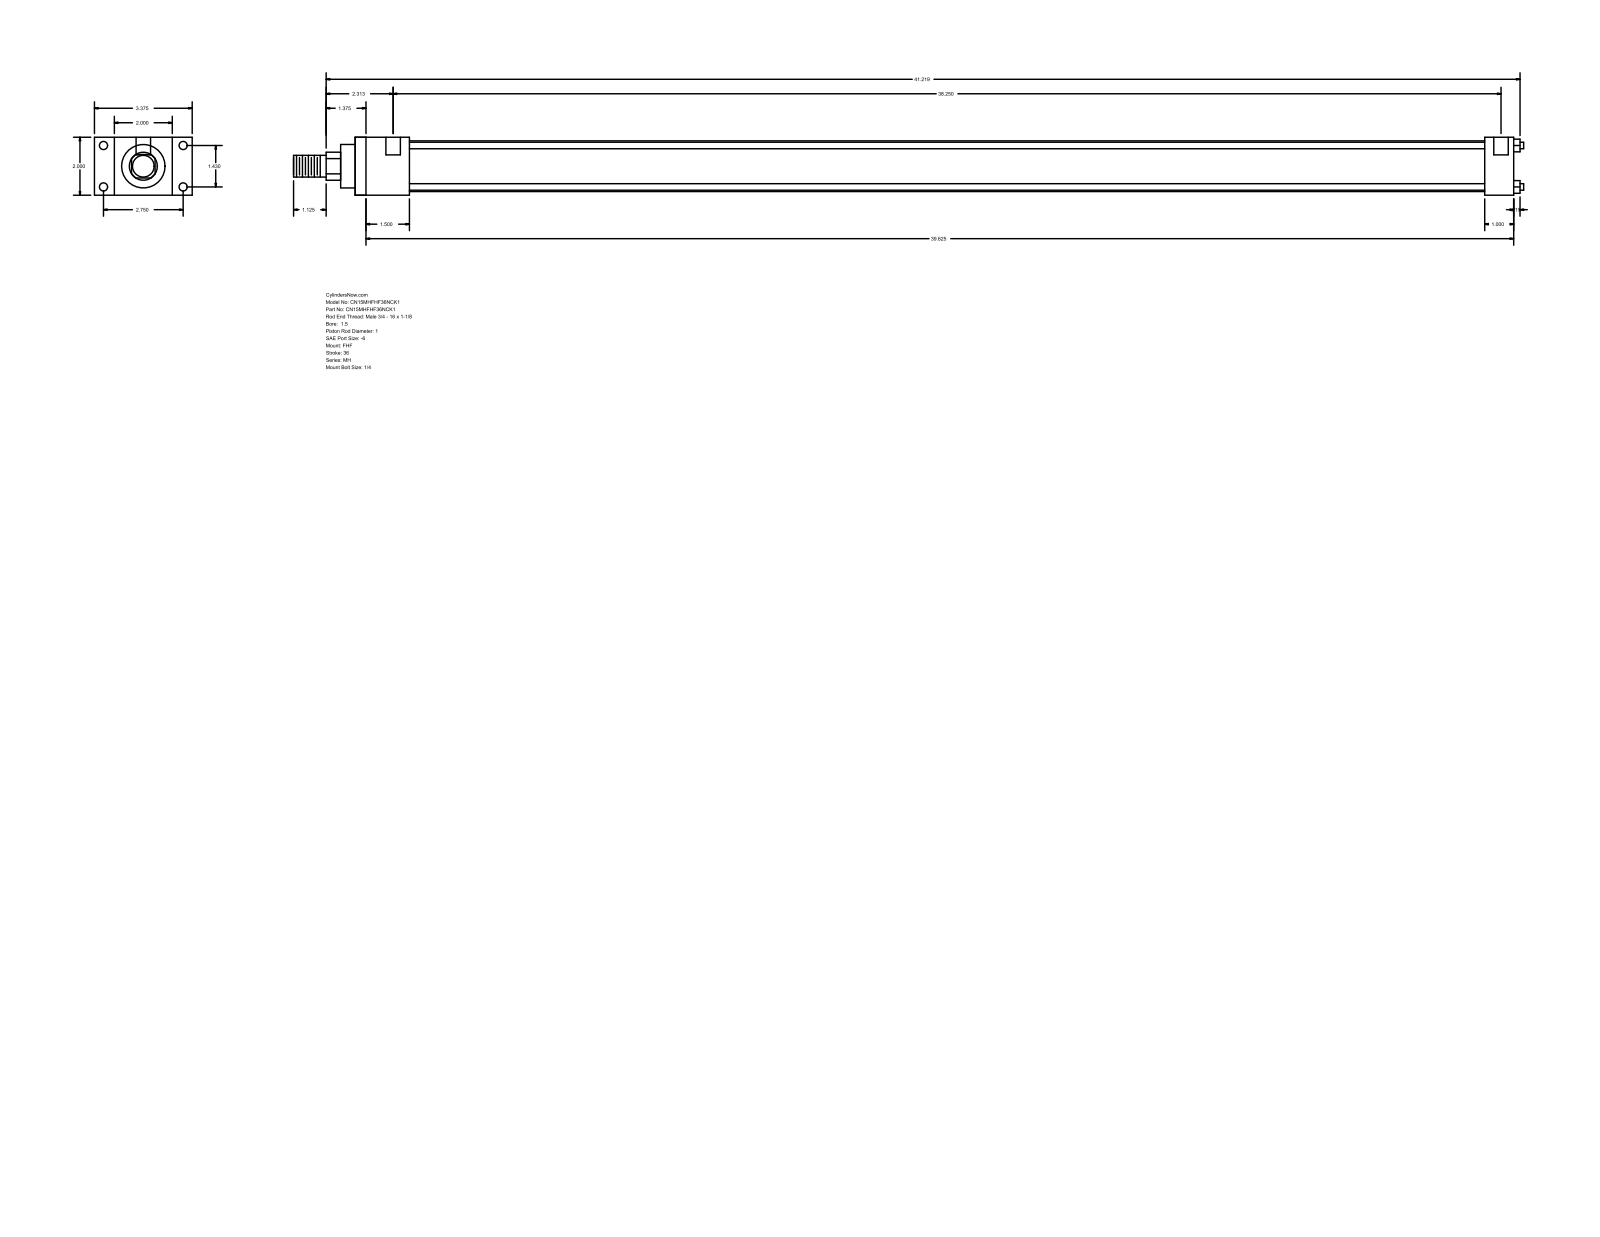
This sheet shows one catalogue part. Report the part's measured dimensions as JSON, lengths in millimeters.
{"part_name": "MH_FHF__0150_1", "step_written_by": "GSSL Pune (CONFIG_CONTROL_DESIGN)", "units": "millimeters", "bodies": {"solids": 0, "faces": 88, "planar": 60, "cylindrical": 28, "other": 0}, "overall_size": [1078.71, 85.72, 50.8], "round_holes": [[5.56, 4], [7.14, 4], [12.7, 2]], "round_bosses_or_shafts": [[5.71, 4], [44.45, 1], [38.1, 1], [25.4, 1], [19.05, 1]], "partial_cylinders_radius": [[12.29, 1]], "face_to_face_distances": [50.8, 17.46, 68.26, 47.63, 85.72, 1016, 968.37, 25.4, 990.6, 942.97], "hole_center_spacings": [36.32, 69.84, 78.72, 974.73, 3.18, 971.55]}
